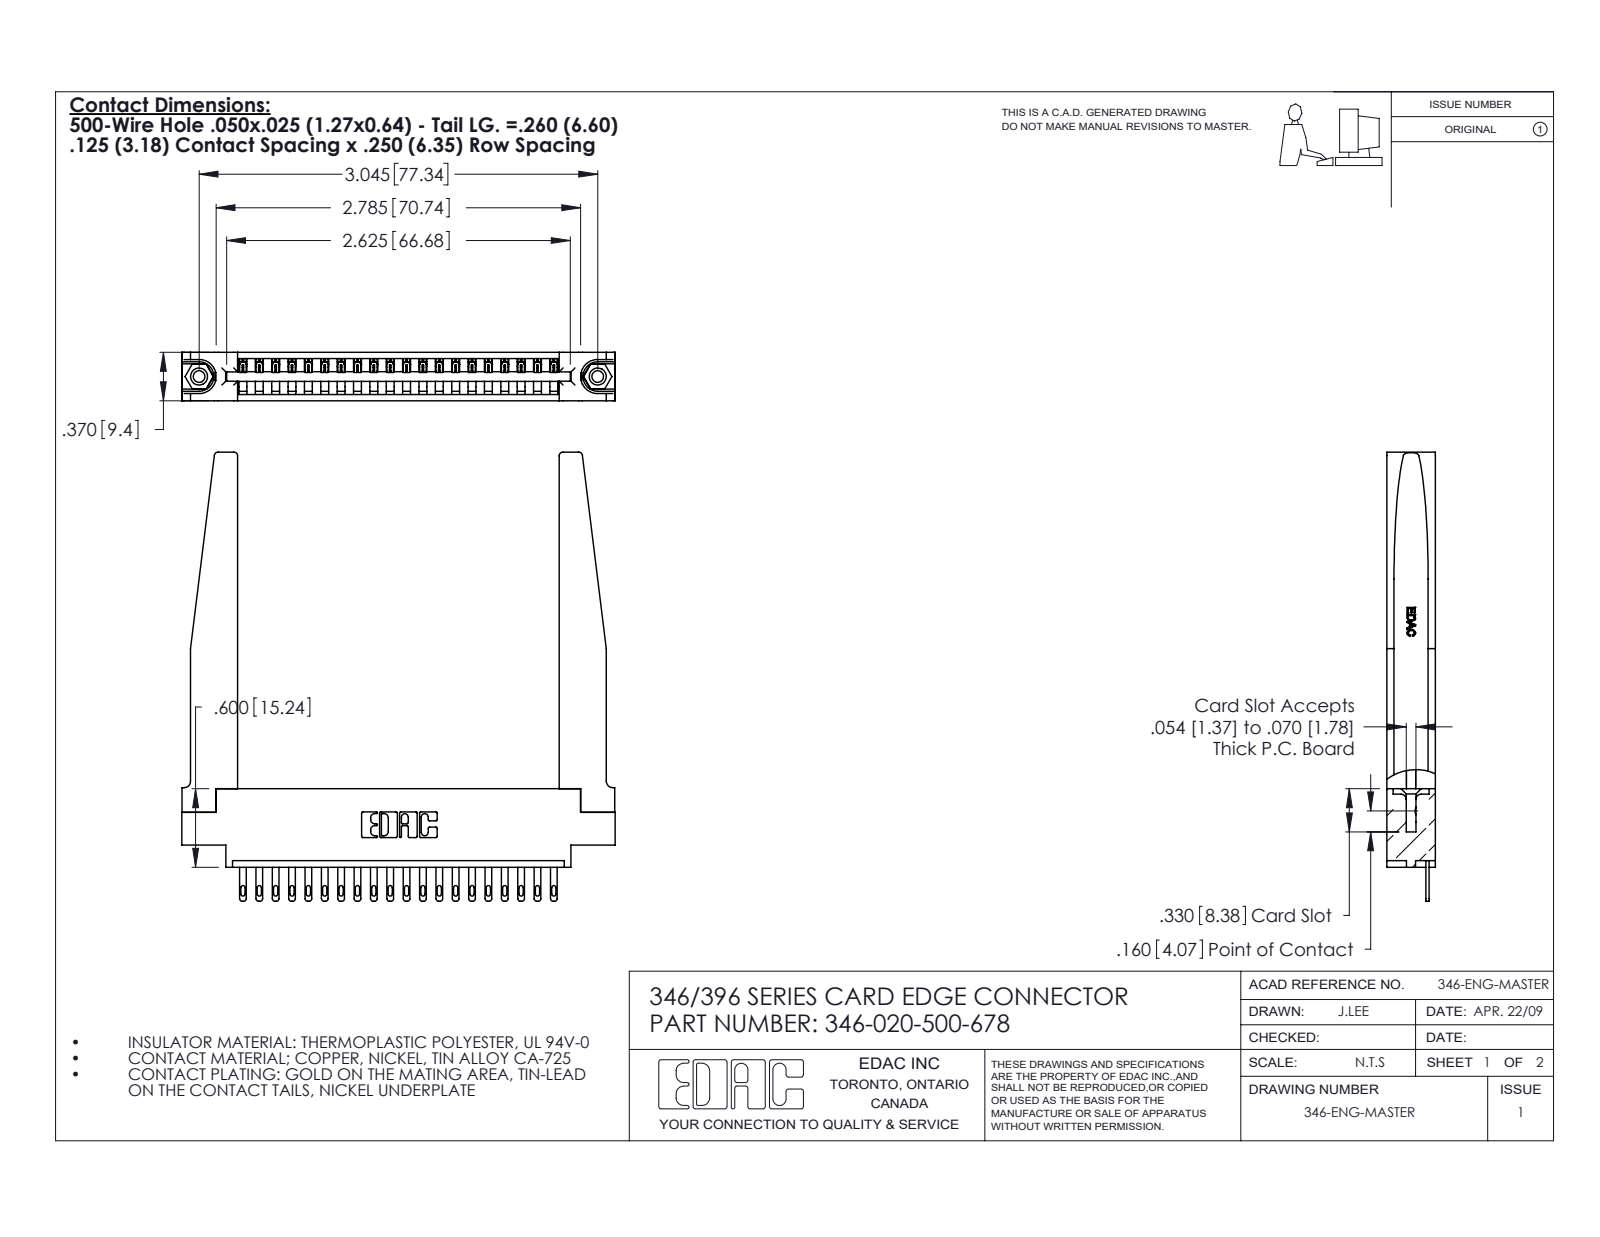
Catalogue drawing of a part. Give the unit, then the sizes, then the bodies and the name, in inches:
Units: inches
Overall size (bounding box): 3.43 × 3.31 × 0.37
Round holes (diameter × count): ⌀0.089 ×2, ⌀0.125 ×2, ⌀0.156 ×2, ⌀0.064 ×1
Round bosses / shafts (diameter × count): ⌀0.155 ×2
Partial cylindrical surfaces — rounded edges, fillets, slot ends (radius × count): R0.006 ×40, R0.016 ×40, R0.02 ×40, R0.01 ×22, R0.03 ×8, R0.007 ×6, R0.031 ×6, R0.026 ×3
Main face-to-face distances: 0.37, 0.072, 0.048, 0.322, 0.15, 0.148, 0.25, 0.298, 0.025, 0.102
Hole centre spacings: 0.246, 2.837, 3.045
Volume: 0.894 in³ · Surface area: 25.13 in²
Bodies: 25 solids, 1454 faces (916 planar, 486 cylindrical, 52 other)
Part name (STEP PRODUCT): 346-220-078_345-220-078; 345-250-001_345-250-001-102; 346 Part_0.170 Offset - 0.156 Dia-TH; 346-020-500-678 (+1 more)
STEP written by: SolidWorks 2020 (CONFIG_CONTROL_DESIGN)
